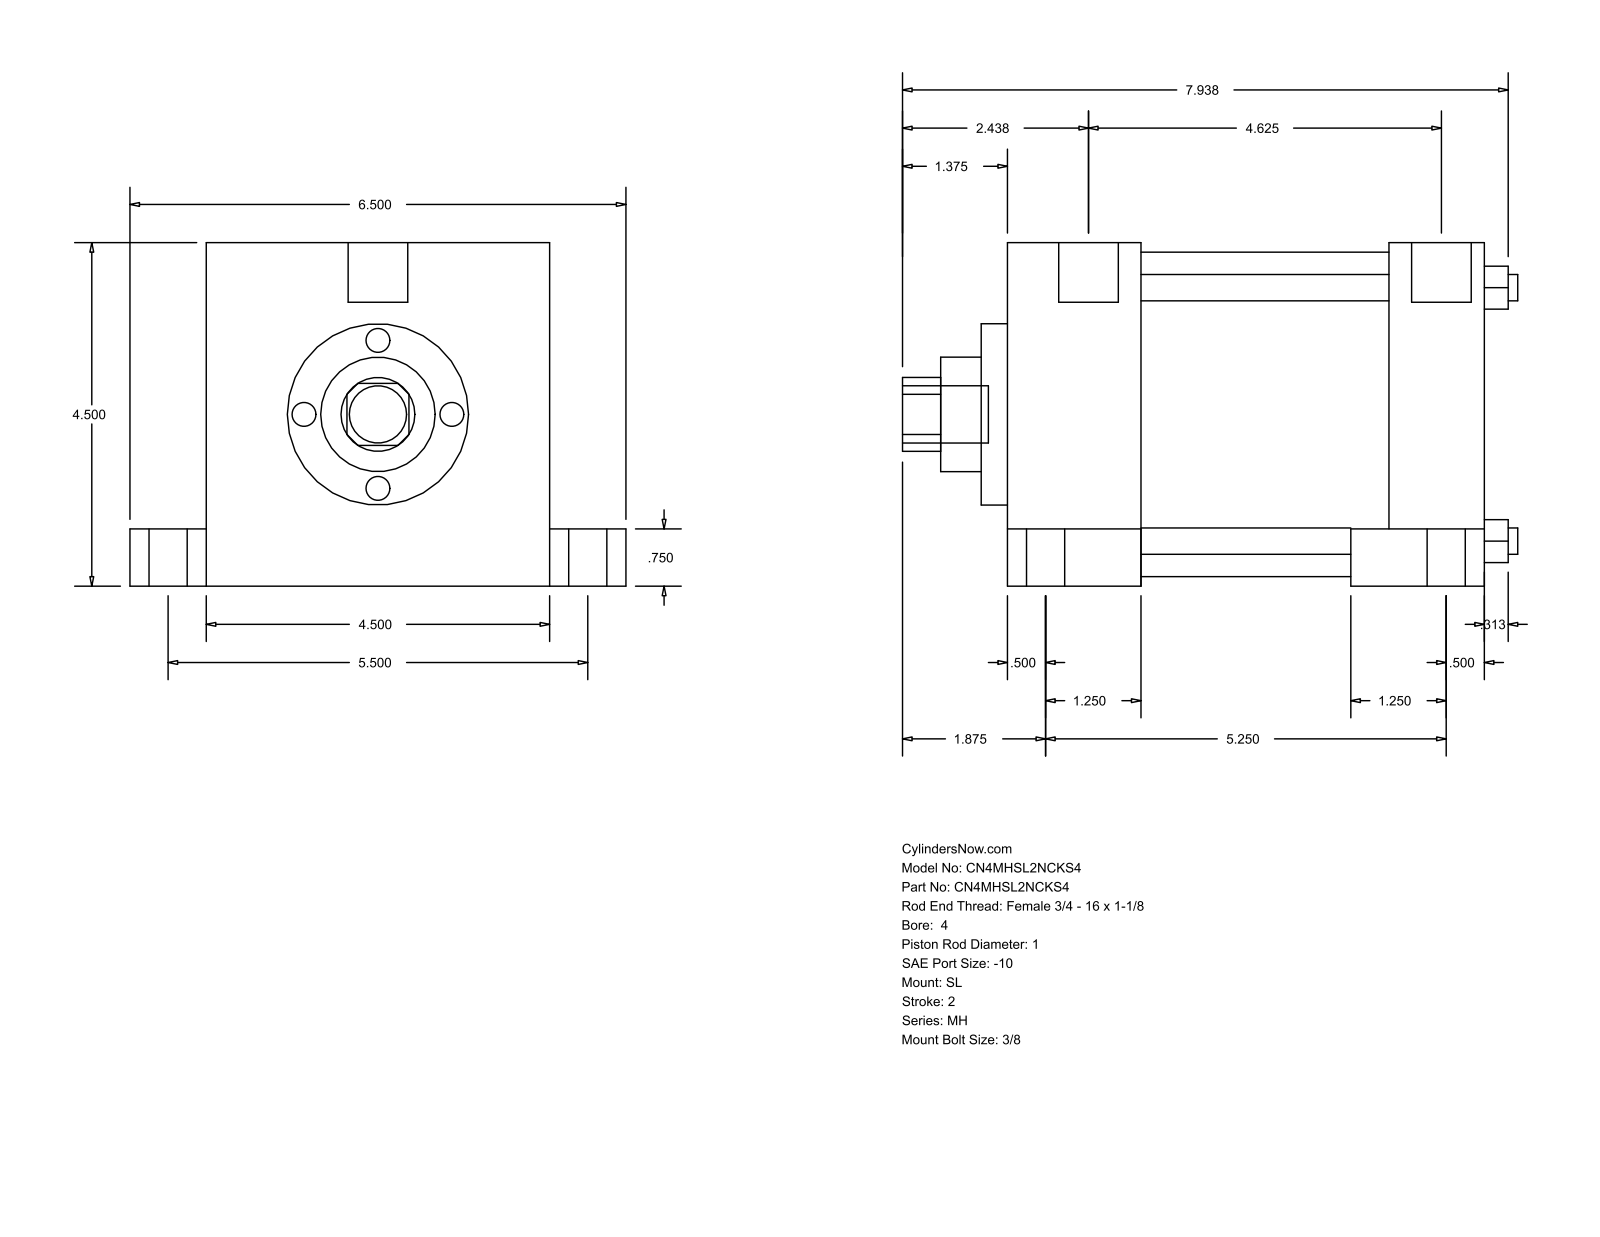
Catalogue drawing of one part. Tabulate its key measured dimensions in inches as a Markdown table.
| quantity | value |
| --- | --- |
| part name | MH_SL__0400_1 |
| STEP written by | GSSL Pune (CONFIG_CONTROL_DESIGN) |
| units | inches |
| bodies | 0 solids, 110 faces (77 planar, 33 cylindrical, 0 other) |
| overall size | 8.063 × 6.5 × 4.5 |
| round holes (diameter × count) | 0.345 × 4, 1 × 1, 1.5 × 1, 2.375 × 1, 4.25 × 1 |
| round bosses / shafts (diameter × count) | 0.75 × 5, 0.5 × 4, 0.344 × 4, 0.781 × 2 |
| partial cylindrical surfaces (radius × count) | 0.484 × 1 |
| main face-to-face distances | 4.5, 6.25, 1.75, 5, 3.25, 1.25, 1, 5.5, 0.75, 3.75 |
| hole center spacings | 2.347, 3.32, 4.695 |
